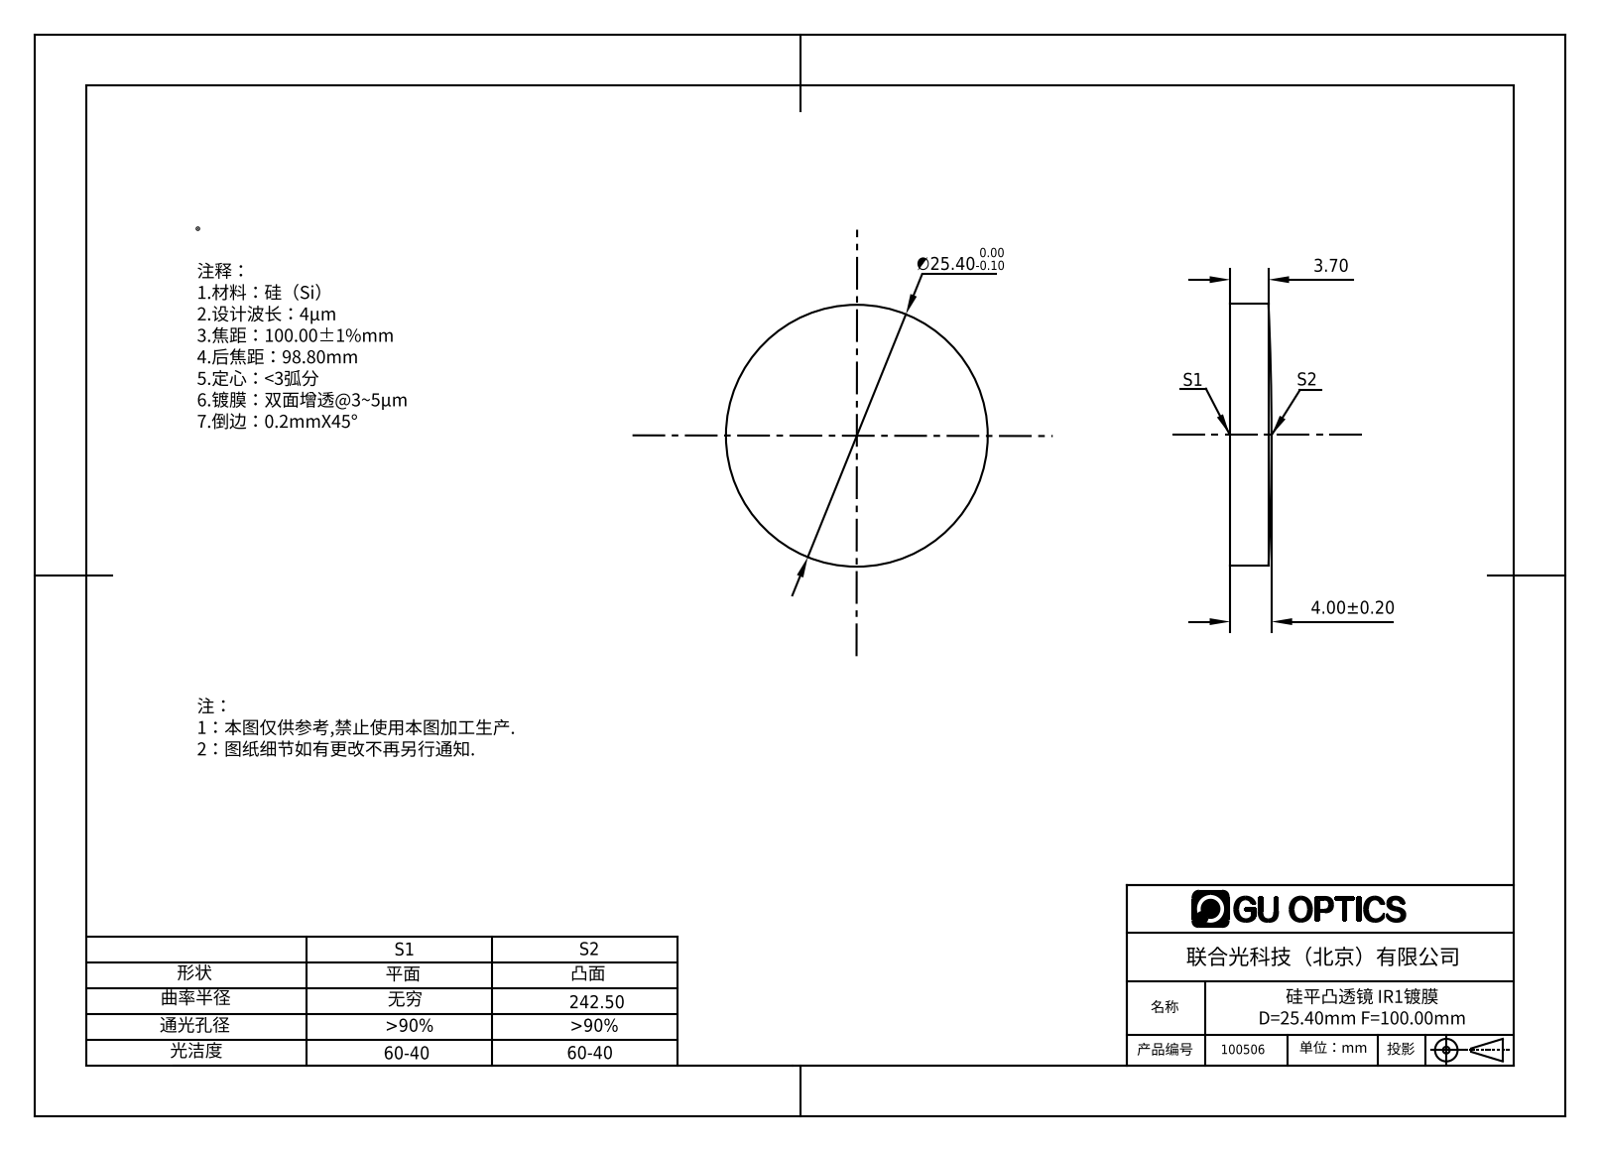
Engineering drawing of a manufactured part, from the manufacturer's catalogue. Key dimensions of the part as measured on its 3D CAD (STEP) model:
Part name (STEP PRODUCT): 100494
STEP written by: SolidWorks 2016 (AUTOMOTIVE_DESIGN)
Units: millimetres
Bodies: 1 solid, 5 faces (1 planar, 2 cylindrical, 2 other)
Overall size (bounding box): 25.4 × 25.4 × 4
Volume: 1 951 mm³ · Surface area: 1 309 mm²
Round bosses / shafts (diameter × count): ⌀25.4 ×1
